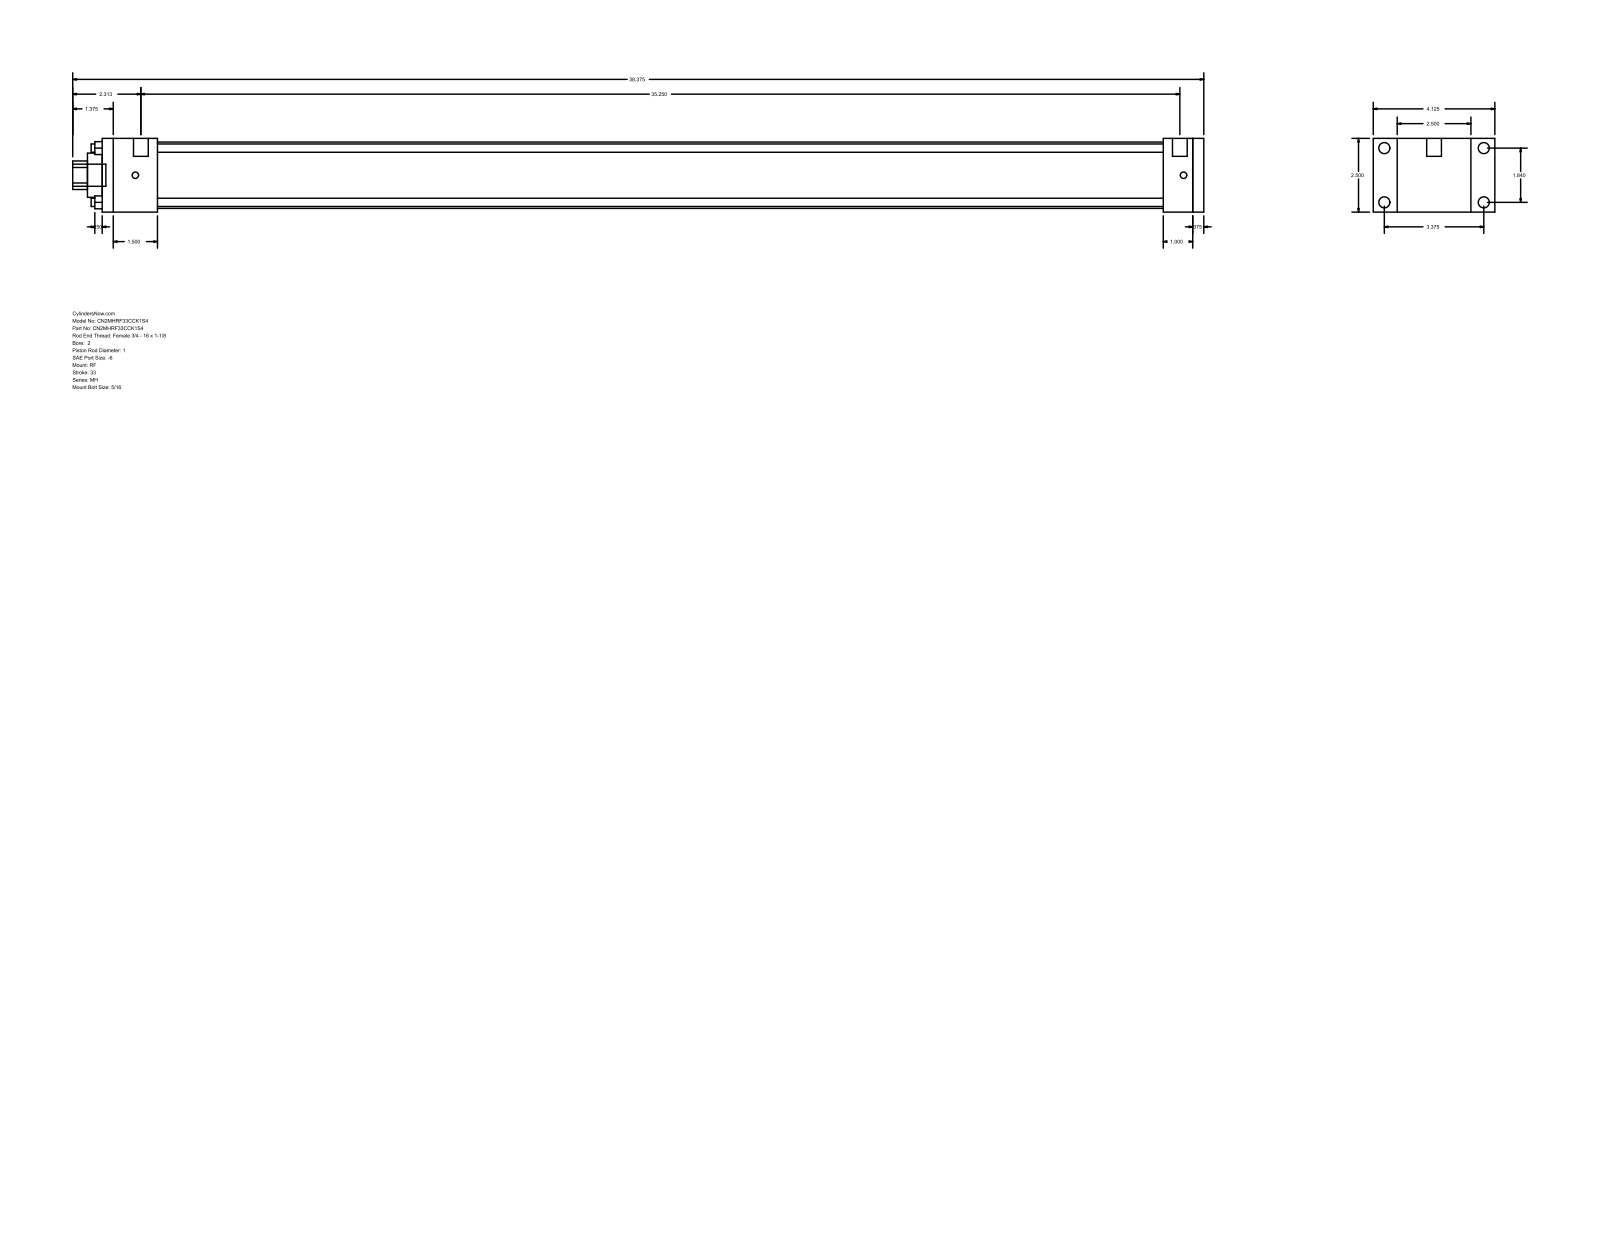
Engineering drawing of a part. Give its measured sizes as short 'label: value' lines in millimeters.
name: MH_RF__0200_1
written by: GSSL Pune (CONFIG_CONTROL_DESIGN)
unit: mm
bodies: 0 solids, 92 faces (64 planar, 28 cylindrical, 0 other)
size: 974.73 × 104.78 × 63.5
holes: 4× ⌀7.14, 1× ⌀25.4, 1× ⌀38.1, 1× ⌀57.15
bosses: 4× ⌀9.53, 4× ⌀5.56, 2× ⌀12.7, 1× ⌀19.05
rounds: 1× R12.29
face distances: 63.5, 949.33, 939.8, 9.53, 20.64, 25.4, 47.63, 914.4, 866.77, 892.17
hole spacings: 33.05, 46.74, 66.1
